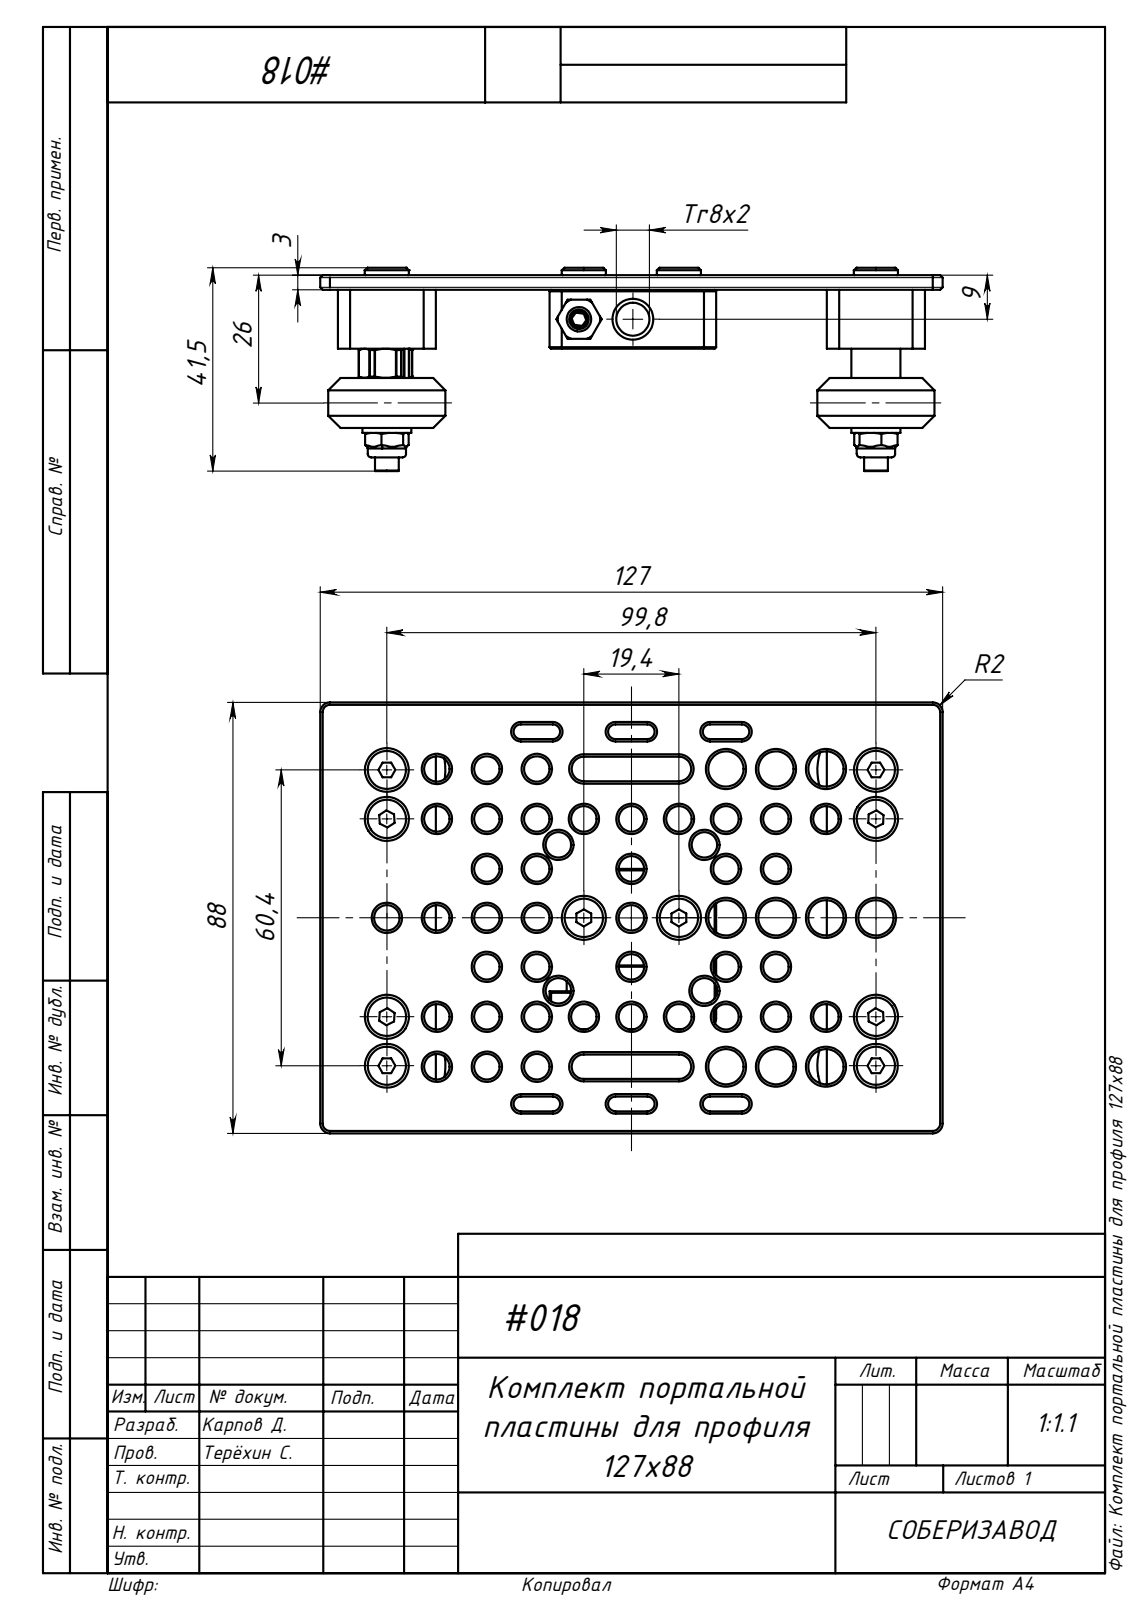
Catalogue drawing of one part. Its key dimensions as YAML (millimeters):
part_name: "A229 Самоконтрящаяся гайка M5_00; A195-Standartnyy-ekstsentrik-6-mm_-dlya-vinta-M5_podrobnaya-model__00; Гайка М5, низкая DIN 439, K32_00; A201 Дистанционная втулка 5х6 мм_00 (+7 more)"
step_written_by: "SolidWorks 2021 (AUTOMOTIVE_DESIGN)"
units: millimeters
bodies: {solids: 46, faces: 1485, planar: 409, cylindrical: 492, other: 584}
overall_size: [127, 88, 41.5]
volume: 98661
surface_area: 64496
round_holes:
  - {diameter: 5.2, count: 55}
  - {diameter: 7.2, count: 17}
  - {diameter: 4.13, count: 6}
  - {diameter: 5, count: 6}
  - {diameter: 4.4, count: 4}
  - {diameter: 5.15, count: 4}
  - {diameter: 13.8, count: 4}
  - {diameter: 14, count: 4}
  - {diameter: 16, count: 4}
  - {diameter: 9.5, count: 2}
  - {diameter: 4, count: 1}
  - {diameter: 4.2, count: 1}
round_bosses_or_shafts:
  - {diameter: 9, count: 6}
  - {diameter: 7.83, count: 6}
  - {diameter: 5, count: 6}
  - {diameter: 23.9, count: 4}
  - {diameter: 10, count: 4}
  - {diameter: 8.95, count: 4}
  - {diameter: 8.6, count: 4}
  - {diameter: 4.85, count: 4}
partial_cylinders:
  - {radius: 0.2, count: 28}
  - {radius: 2.5, count: 17}
  - {radius: 1, count: 12}
  - {radius: 1.5, count: 12}
  - {radius: 0.3, count: 6}
  - {radius: 2, count: 4}
face_to_face_distances: [3, 12, 15, 20, 99.8, 5, 4.65, 5.2, 0.35, 6]
hole_center_spacings: [10.2, 14.42, 22.81, 20.2, 22.41, 9.7, 20.4, 21.83]
